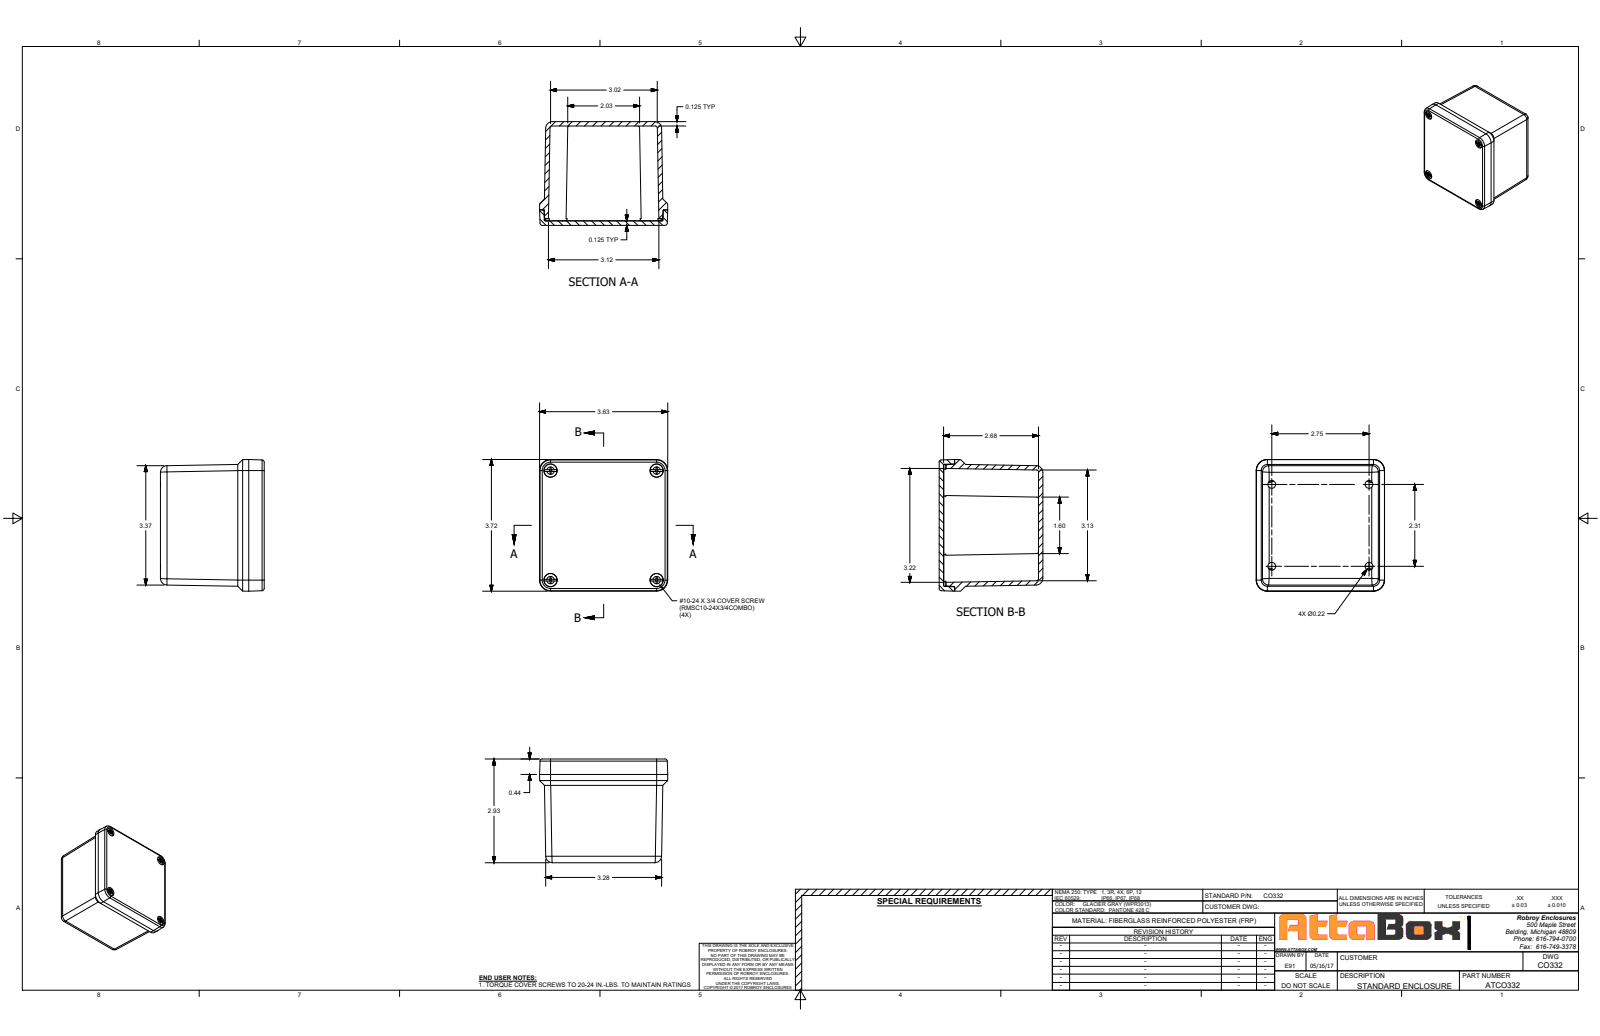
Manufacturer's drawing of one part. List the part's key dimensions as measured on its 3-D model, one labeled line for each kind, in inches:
Part name (STEP PRODUCT): CO332
STEP written by: SolidWorks 2018 (AUTOMOTIVE_DESIGN)
Units: inches
Bodies: 11 solids, 353 faces (153 planar, 108 cylindrical, 92 other)
Overall size (bounding box): 3.721 × 3.625 × 2.933
Volume: 10.81 in³ · Surface area: 148.6 in²
Round holes (diameter × count): ⌀0.219 ×8, ⌀0.159 ×4, ⌀0.19 ×4, ⌀0.375 ×4
Round bosses / shafts (diameter × count): ⌀0.371 ×4, ⌀0.27 ×4, ⌀0.177 ×4
Partial cylindrical surfaces — rounded edges, fillets, slot ends (radius × count): R0.031 ×20, R0.012 ×16, R0.048 ×8, R0.062 ×4, R0.176 ×4, R0.22 ×4, R0.313 ×4, R0.187 ×3
Main face-to-face distances: 0.122, 0.125, 0.125, 2.807, 2.933, 2.683, 2.808, 0.438, 2.495, 2.37
Hole centre spacings: 0.41, 2.706, 2.901, 3.946, 2.313, 2.75, 3, 3.094
